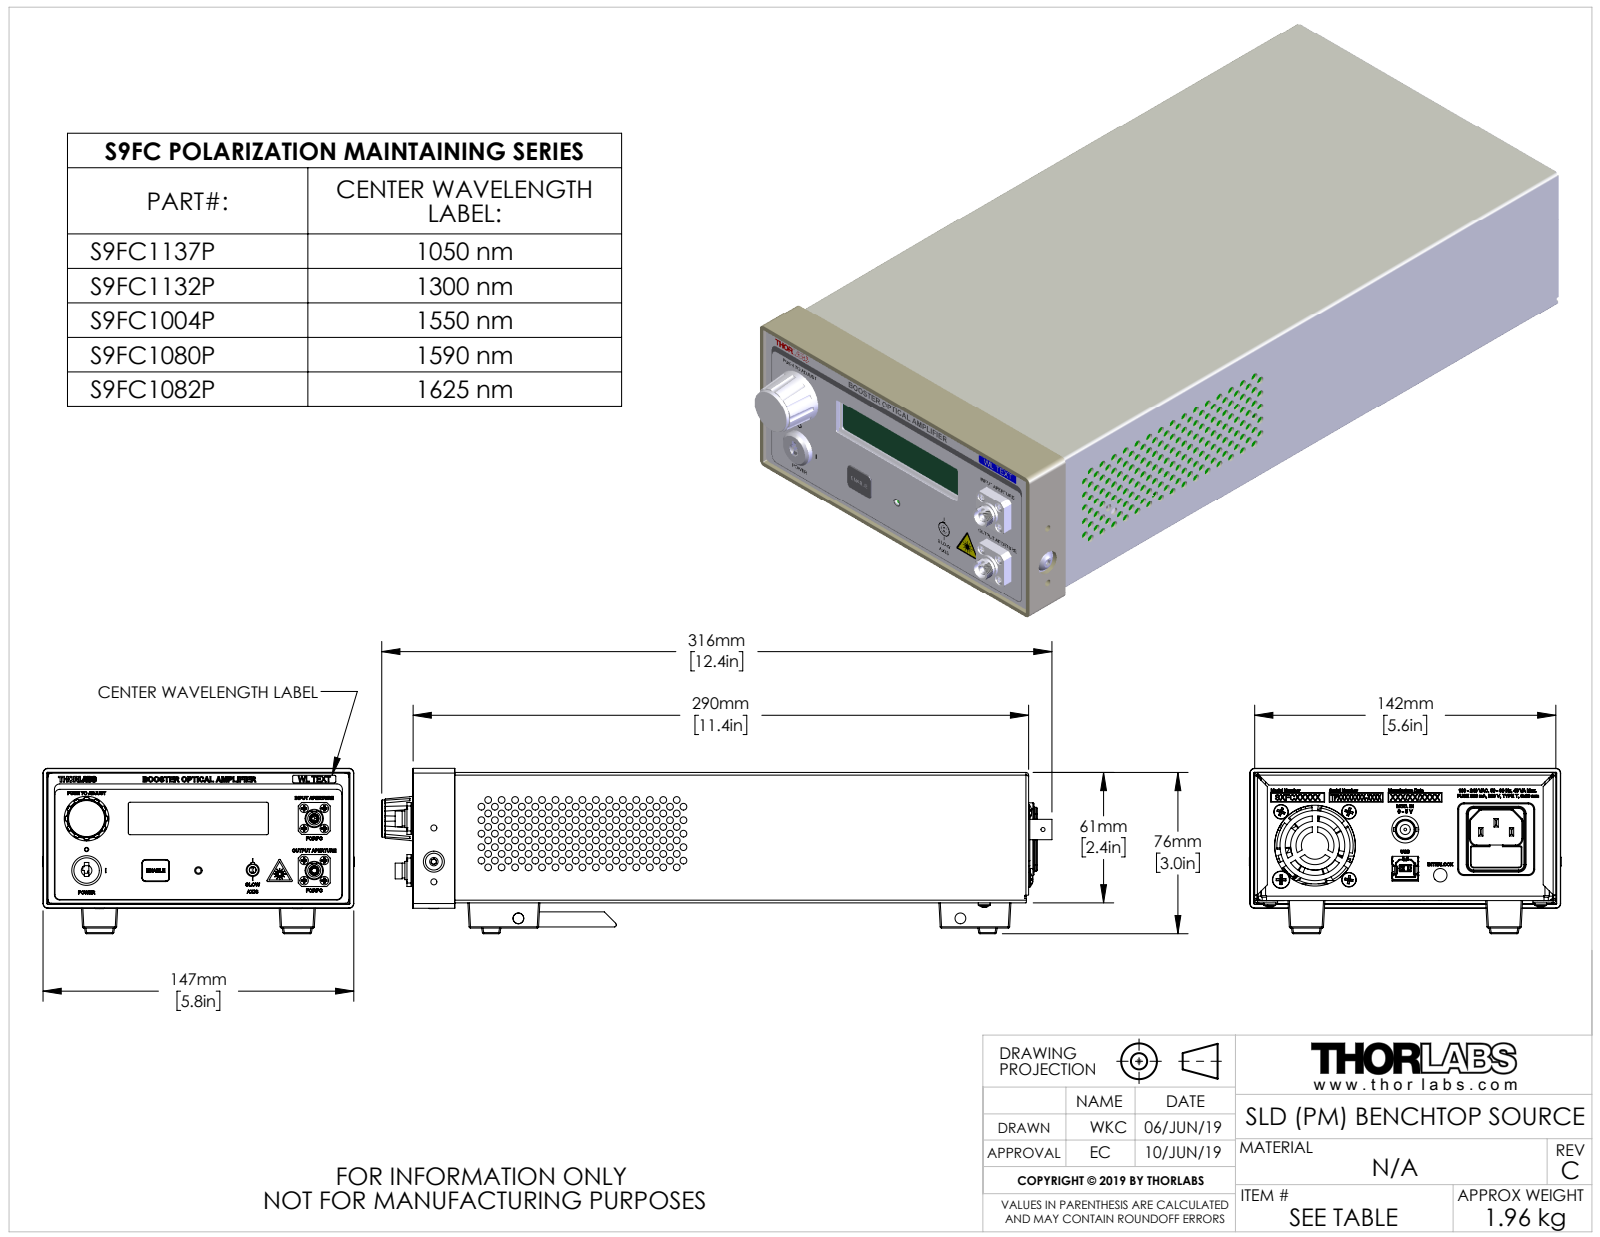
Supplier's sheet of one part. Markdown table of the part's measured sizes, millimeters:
| quantity | value |
| --- | --- |
| part name | 19914-E0W |
| STEP written by | SolidWorks 2018 (CONFIG_CONTROL_DESIGN) |
| units | millimeters |
| bodies | 0 solids, 13368 faces (7714 planar, 1243 cylindrical, 4411 other) |
| overall size | 316 × 147 × 78 |
| round holes (diameter × count) | 3.2 × 170, 0.9 × 44, 1 × 16, 1 × 16, 0.8 × 14, 4 × 12, 3 × 9, 1.8 × 8, 2.2 × 8, 2.6 × 8, 3.1 × 8, 3.6 × 7 |
| round bosses / shafts (diameter × count) | 3.8 × 9, 4.2 × 8, 4.2 × 8, 3 × 8, 2.2 × 8, 3.5 × 7, 6.9 × 6, 0.5 × 6 |
| partial cylindrical surfaces (radius × count) | 0.5 × 51, 0.6 × 48, 0.1 × 32, 0.3 × 20, 1.3 × 17, 0.3 × 15, 3 × 14, 0.5 × 9 |
| main face-to-face distances | 1, 1.6, 60.4, 6.4, 59.4, 57.8, 58.8, 7.9, 51.5, 52.5 |
| hole center spacings | 31.8, 6.4, 12.7, 25.4, 19.1, 26.2, 28.4, 38.1 |
